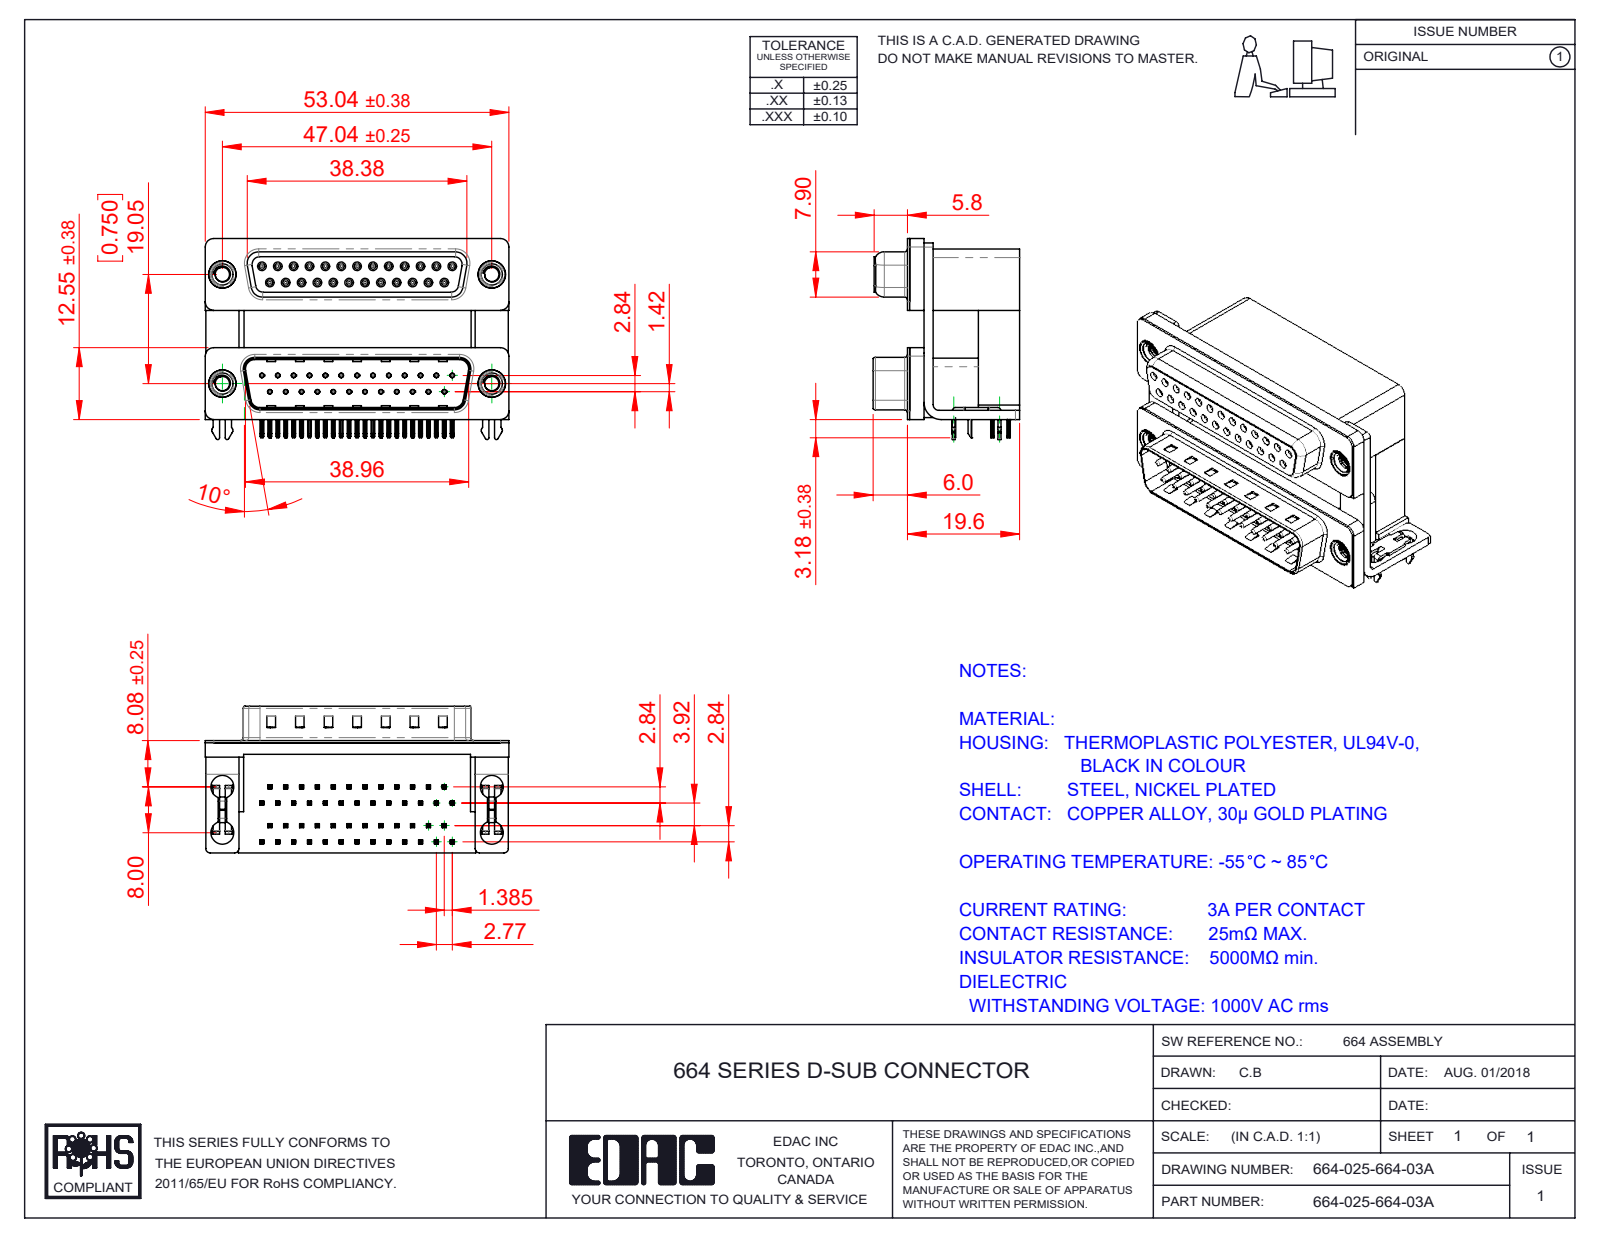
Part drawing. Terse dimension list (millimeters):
name: 664 Housing Lower_25 Contacts; 664 Contact Top Upper_M; 664 Shell Receptacle_25 Contacts; 664 Housing Upper_25 Contacts M (+8 more)
written by: SolidWorks 2020 (CONFIG_CONTROL_DESIGN)
unit: mm
bodies: 63 solids, 6359 faces (3359 planar, 1601 cylindrical, 1399 other)
size: 53.04 × 35.1 × 25.6
volume: 22 487 mm³; area: 24 318 mm²
holes: 50× ⌀0.8, 25× ⌀0.35, 25× ⌀0.9, 8× ⌀4, 4× ⌀2.5, 4× ⌀3.5, 4× ⌀4.8, 4× ⌀5
bosses: 25× ⌀1.2, 25× ⌀0.75, 4× ⌀4.9, 4× ⌀4.75, 4× ⌀3.9
rounds: 202× R0.1, 110× R0.25, 100× R0.15, 50× R0.12, 50× R0.35, 25× R0.34, 16× R0.5, 14× R1.5
face distances: 0.4, 19.2, 7.2, 12, 10.69, 16.7, 9.5, 2.5, 2.84, 18.71
hole spacings: 2.77, 3.16, 5.54, 8.31, 11.08, 13.85, 16.62, 5.03
